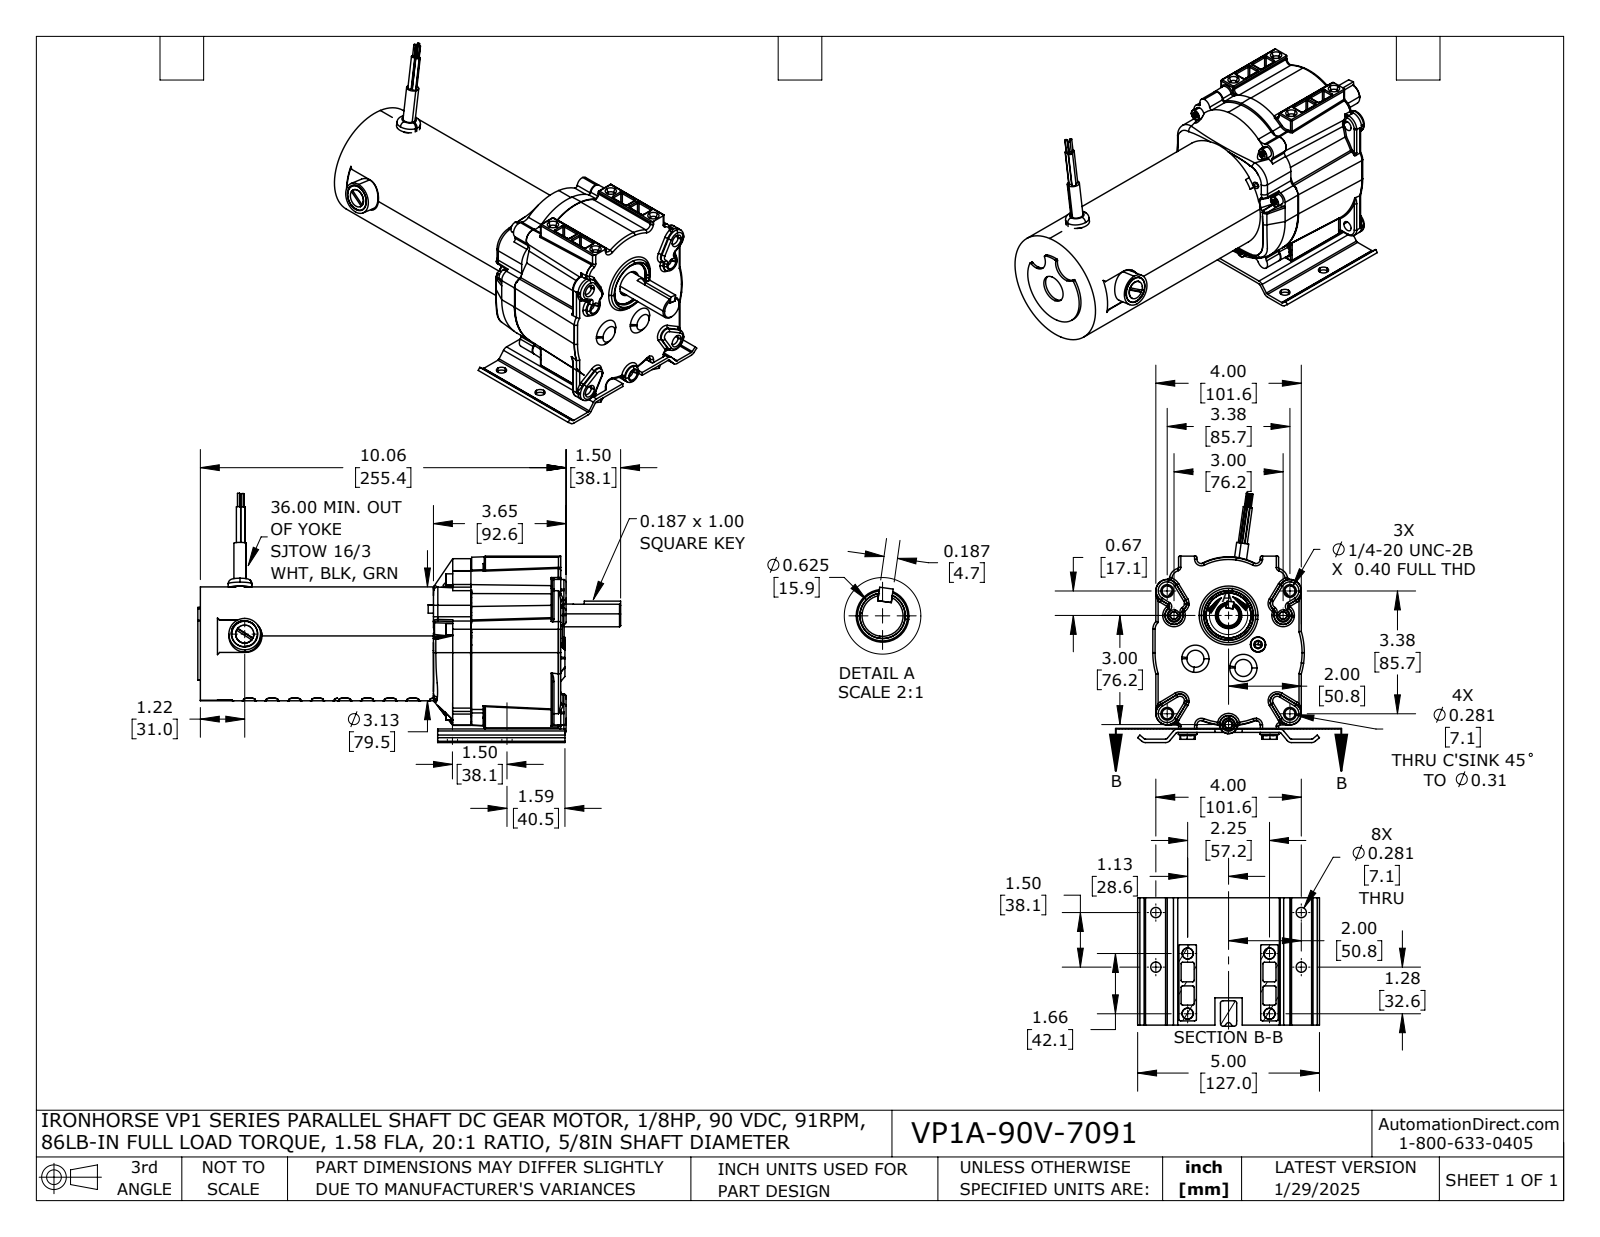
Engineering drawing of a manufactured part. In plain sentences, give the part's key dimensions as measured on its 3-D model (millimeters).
The part is named "VP1A-90V-7091". Its 3-D file was written by "SolidWorks 2024 (AUTOMOTIVE_DESIGN)". It is 10 solids with 2472 faces: 654 planar, 701 cylindrical and 1117 other. Overall it measures 295.3 by 174.1 by 127 millimeters. Its volume is 1 621 000 cubic millimeters and its surface area 222 800 square millimeters. Round holes: 12 of diameter 7.1, 5 of diameter 5.5, 3 of diameter 4, 3 of diameter 5.3, 2 of diameter 3.4, 2 of diameter 4.2, 2 of diameter 5.2, 2 of diameter 10.1, 2 of diameter 17.5, 2 of diameter 22.2, 1 of diameter 19.1, 1 of diameter 20.7. Round bosses or shafts: 5 of diameter 7.8, 5 of diameter 4.8, 4 of diameter 13, 4 of diameter 7.6, 3 of diameter 3, 3 of diameter 1.5, 2 of diameter 22.2, 2 of diameter 18.6. Partial cylindrical surfaces (rounded edges, fillets, slot ends): 52 of radius 0.8, 38 of radius 0.8, 23 of radius 1.6, 18 of radius 3, 18 of radius 4, 10 of radius 4.8, 9 of radius 3.8, 9 of radius 4.1. The main face-to-face distances are 2.4, 62.2, 88.9, 26.7, 239.8, 177.6, 150.9, 11.9, 177, 251.7. The hole center spacings are 38.1, 85.7, 43, 12.5, 17.7, 31.1, 36.2, 39.4.
